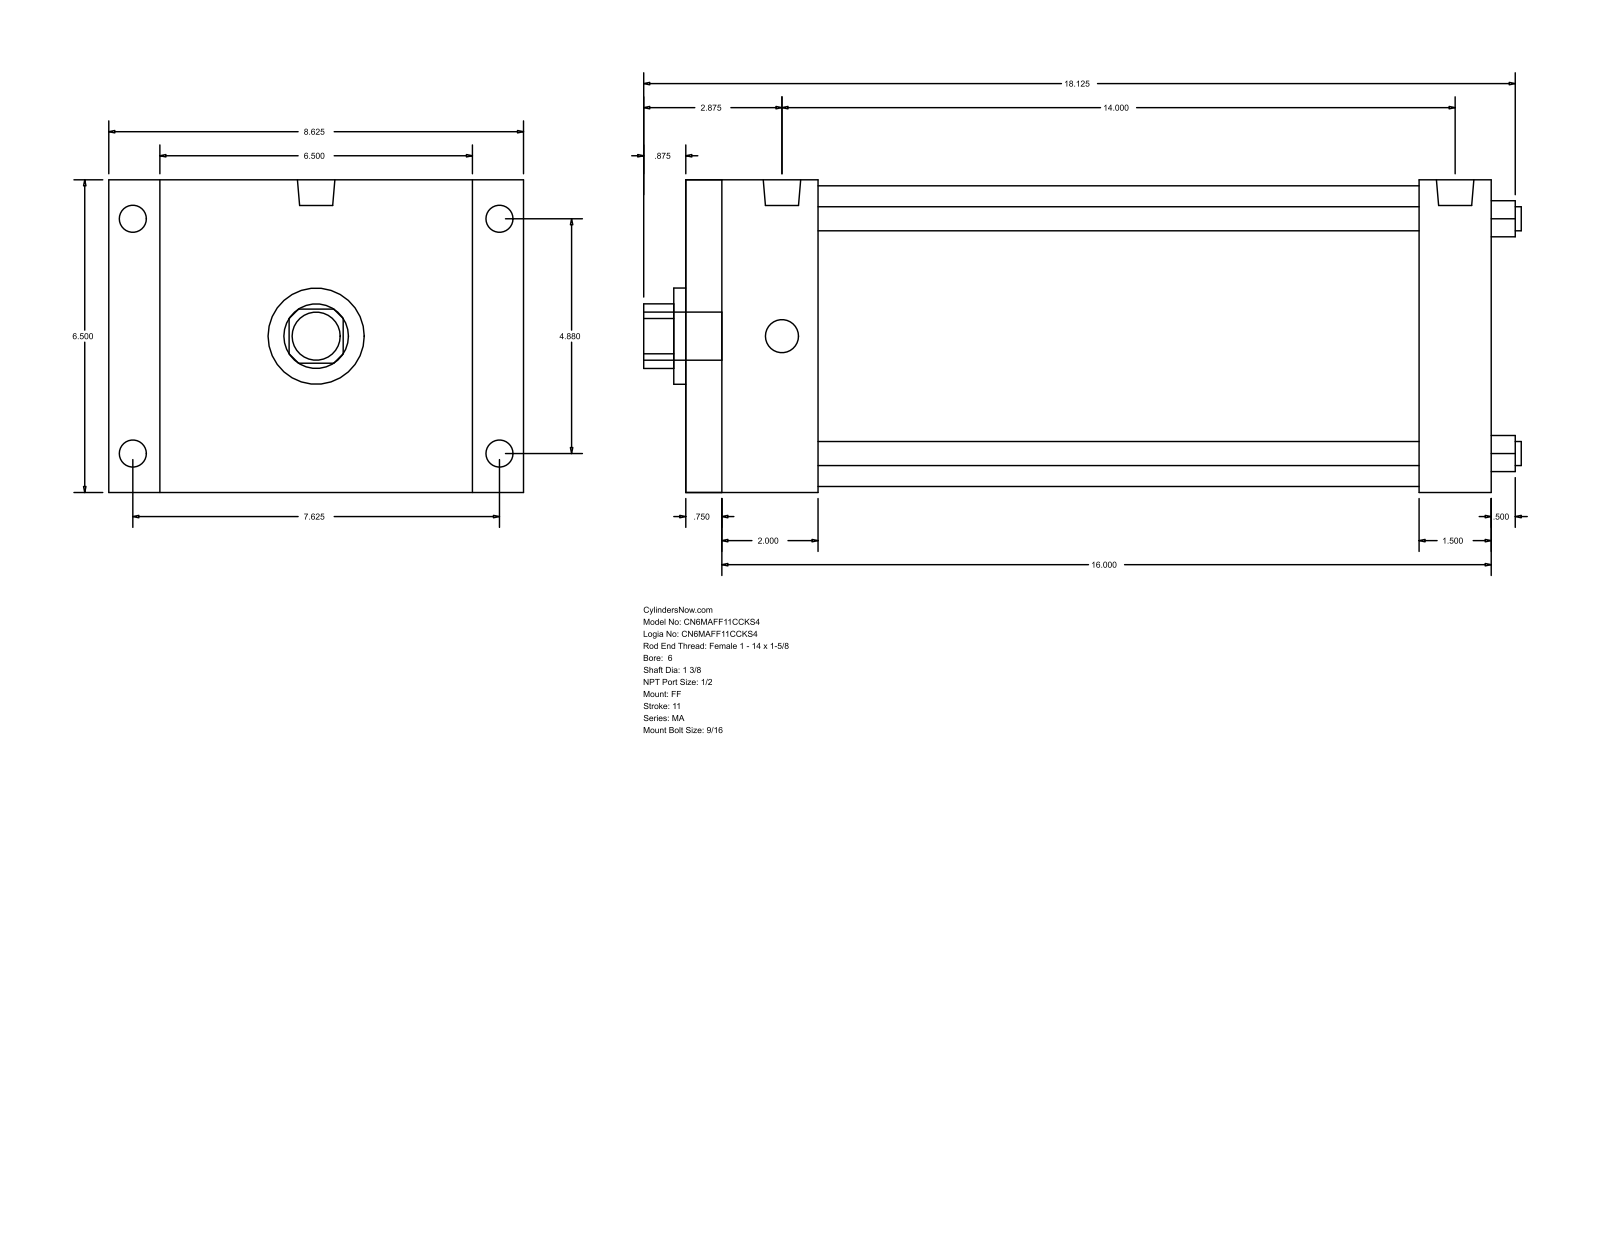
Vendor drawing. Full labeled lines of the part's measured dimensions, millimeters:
Part name (STEP PRODUCT): MA_FF__0600_1.375
STEP written by: GSSL Pune (CONFIG_CONTROL_DESIGN)
Units: millimetres
Bodies: 0 solids, 92 faces (64 planar, 28 cylindrical, 0 other)
Overall size (bounding box): 463.55 × 219.07 × 165.1
Round holes (diameter × count): ⌀12.7 ×4, ⌀34.92 ×1, ⌀50.8 ×1, ⌀158.75 ×1
Round bosses / shafts (diameter × count): ⌀17.46 ×4, ⌀14.29 ×4, ⌀19.77 ×2, ⌀25.4 ×1
Partial cylindrical surfaces — rounded edges, fillets, slot ends (radius × count): R17.06 ×1
Main face-to-face distances: 165.1, 425.45, 15.87, 409.58, 66.67, 50.8, 358.78, 387.34, 371.47, 320.67
Hole centre spacings: 87.65, 123.96, 175.31
